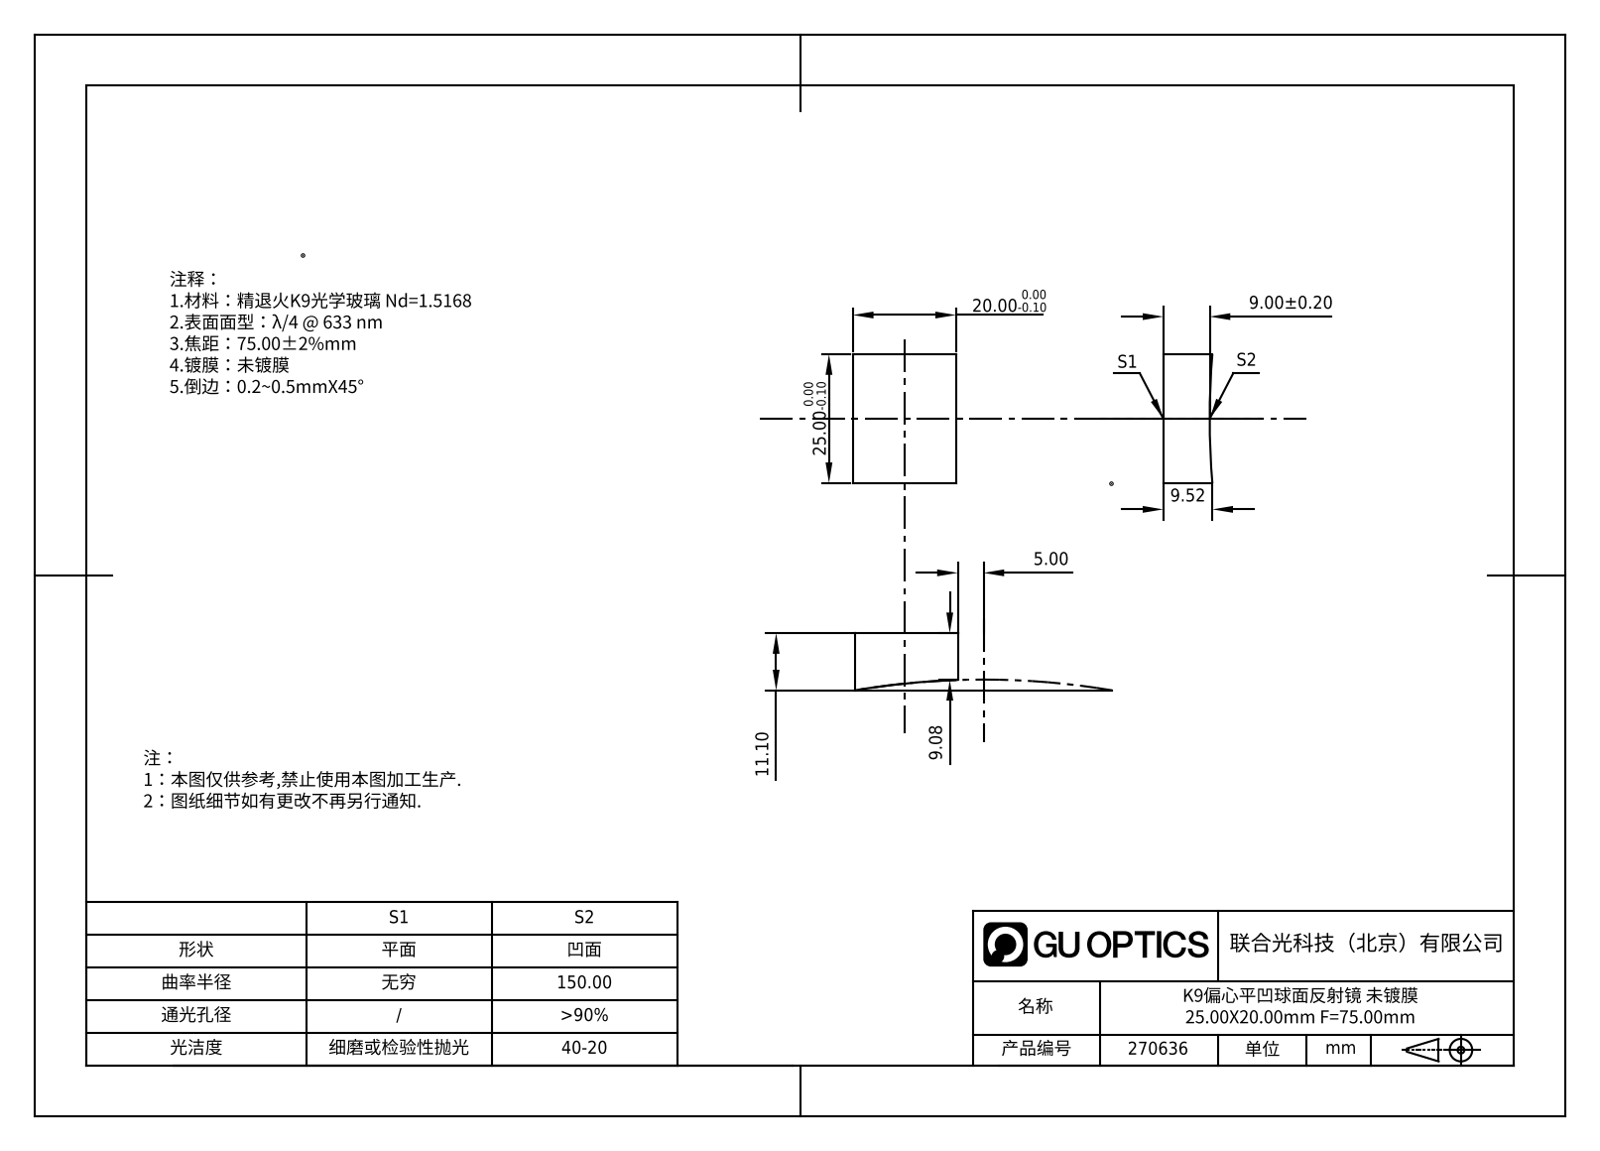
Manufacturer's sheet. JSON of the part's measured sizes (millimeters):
{"part_name": "270636", "step_written_by": "SolidWorks 2020 (CONFIG_CONTROL_DESIGN)", "units": "millimeters", "bodies": {"solids": 1, "faces": 7, "planar": 5, "cylindrical": 0, "other": 2}, "overall_size": [25, 20, 11.63], "volume_mm3": 5020, "surface_area_mm2": 1932, "face_to_face_distances": [20, 25]}
